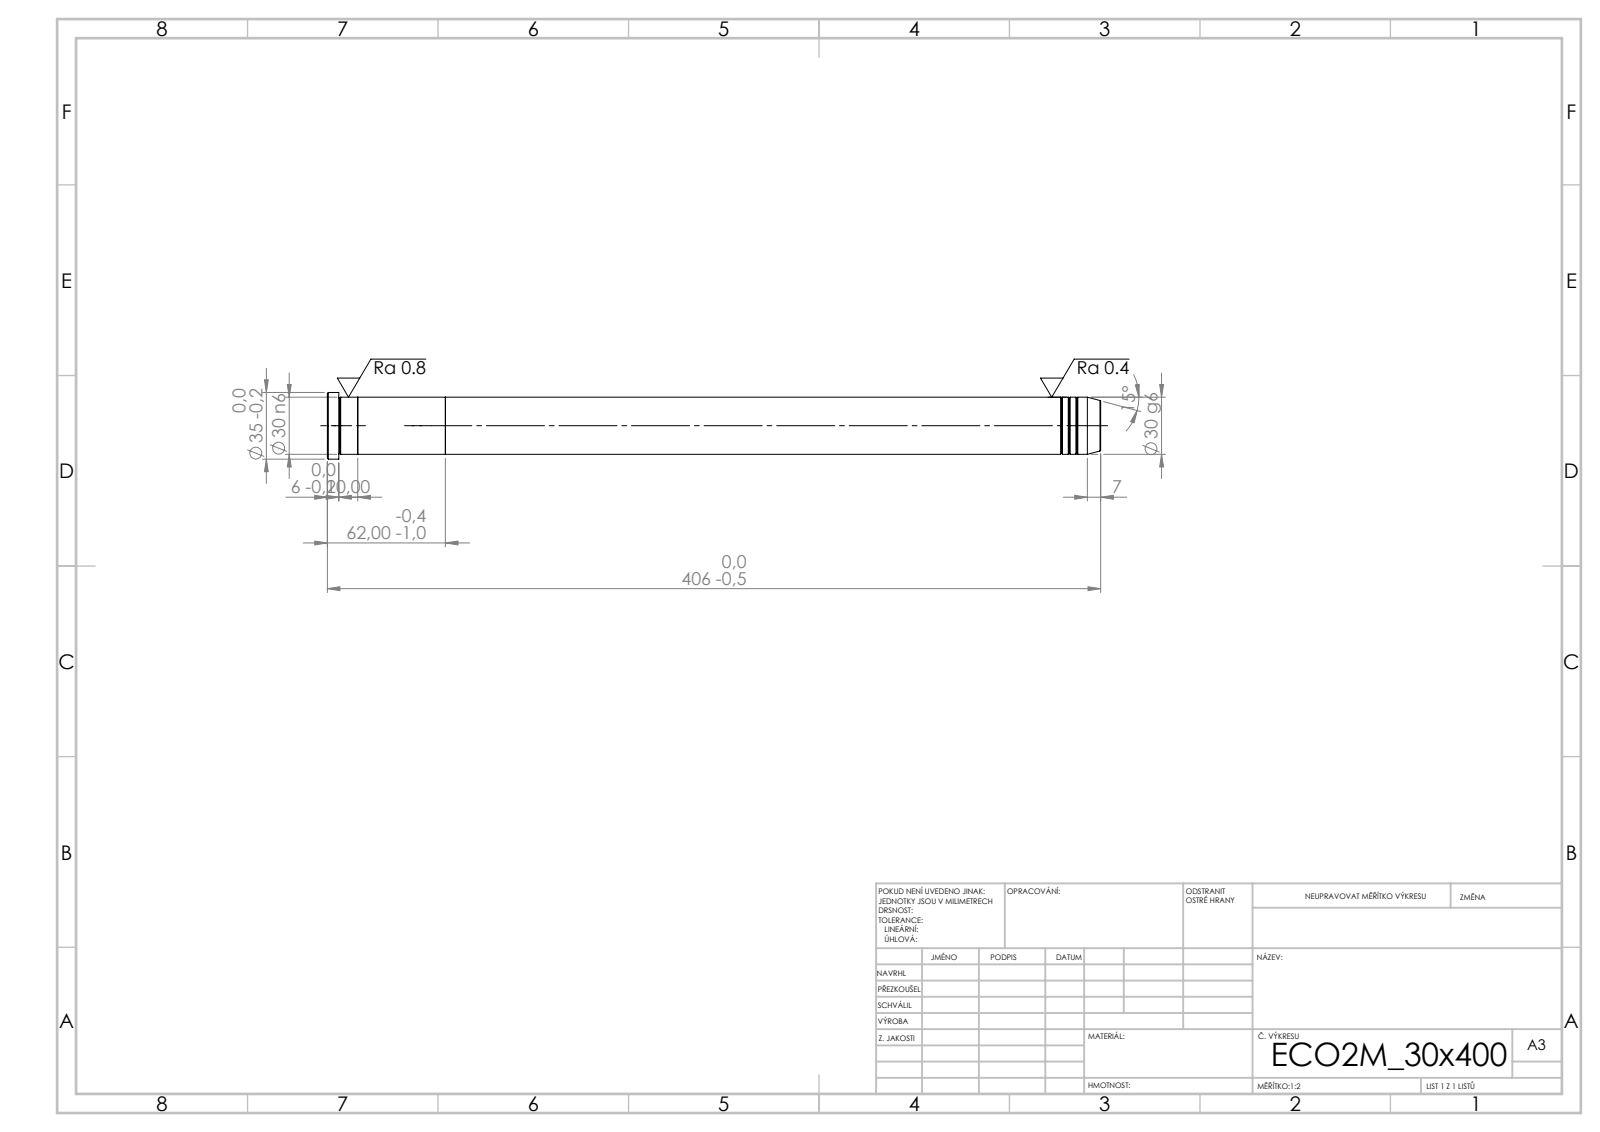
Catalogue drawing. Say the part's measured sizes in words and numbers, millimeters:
Its 3-D file was written by "SolidWorks 2019 (CONFIG_CONTROL_DESIGN)". It is 3 solids with 43 faces: 7 planar, 14 cylindrical and 22 other. Overall it measures 406 by 35 by 35 millimeters. Its volume is 287 761 cubic millimeters and its surface area 43 086 square millimeters. Round bosses or shafts: 1 of diameter 35, 1 of diameter 30. The main face-to-face distances are 46, 62, 16, 344, 390, 406, 400, 56, 10, 6.
